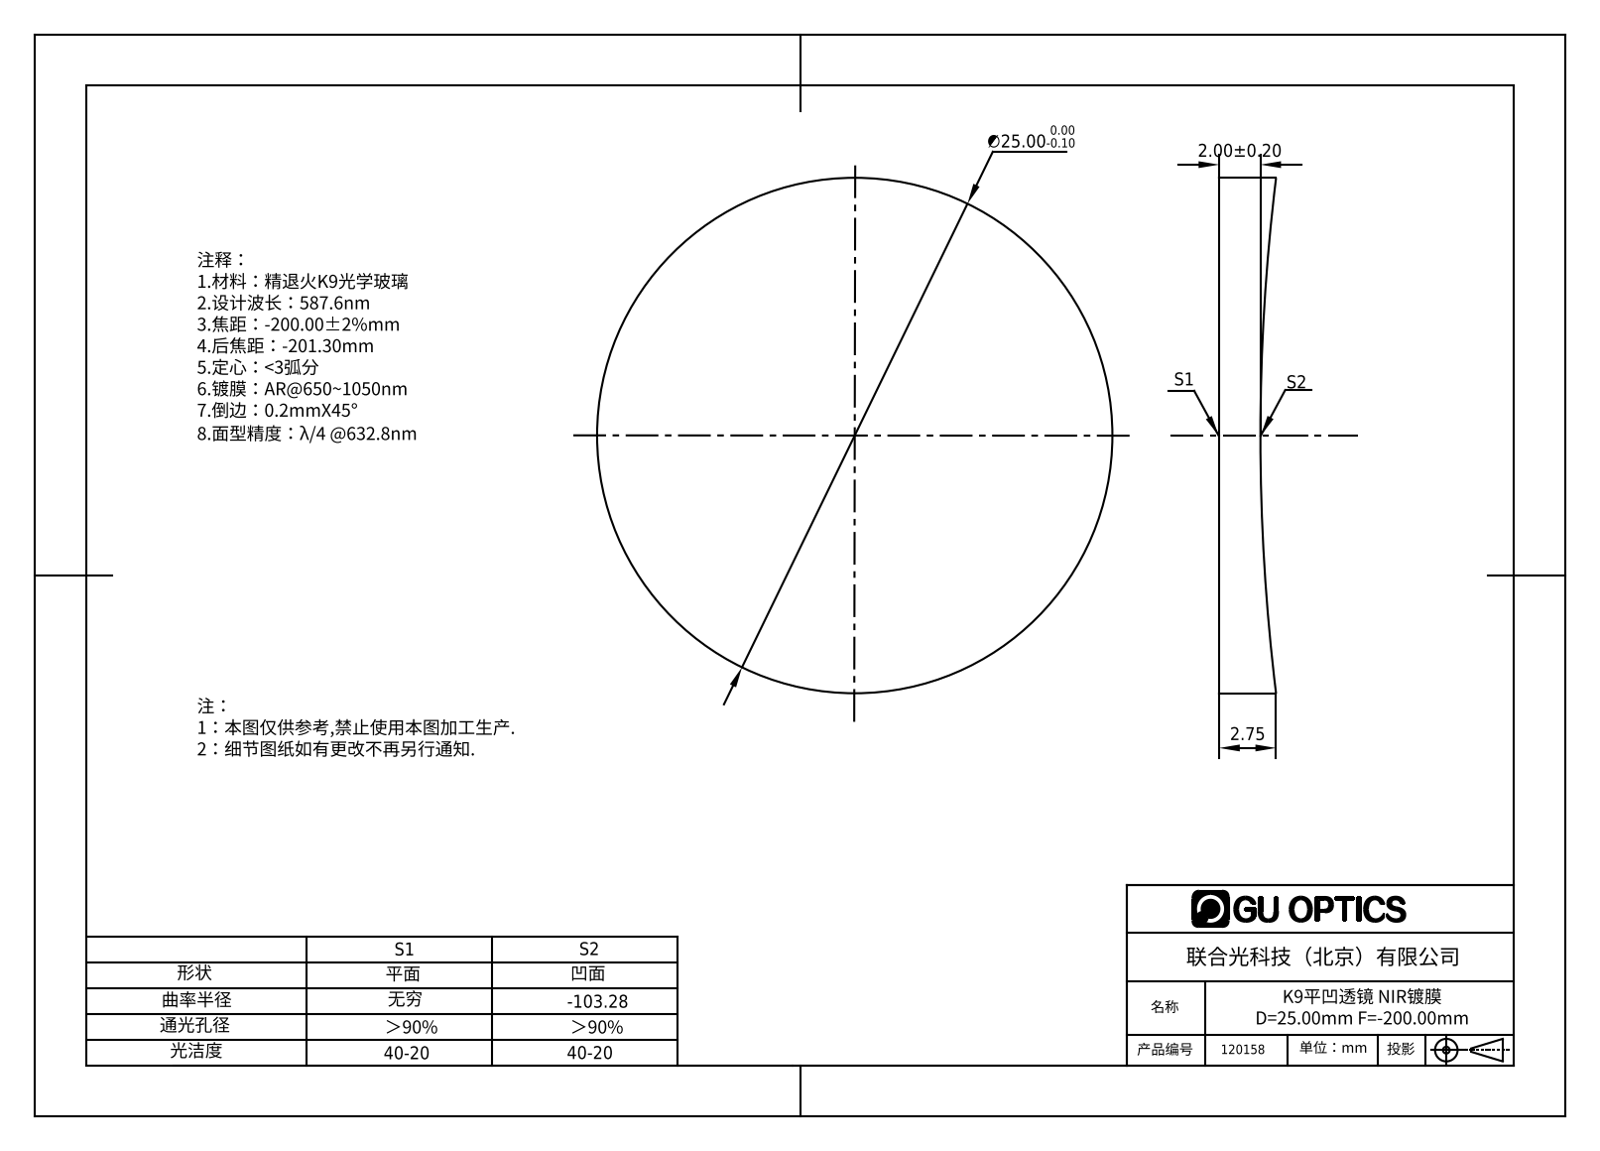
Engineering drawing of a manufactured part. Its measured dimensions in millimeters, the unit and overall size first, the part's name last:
Units: millimetres
Overall size (bounding box): 25 × 25 × 2.76
Round bosses / shafts (diameter × count): ⌀25 ×1
Volume: 1 168 mm³ · Surface area: 1 200 mm²
Bodies: 1 solid, 5 faces (1 planar, 2 cylindrical, 2 other)
Part name (STEP PRODUCT): 120158
STEP written by: SolidWorks 2016 (AUTOMOTIVE_DESIGN)
